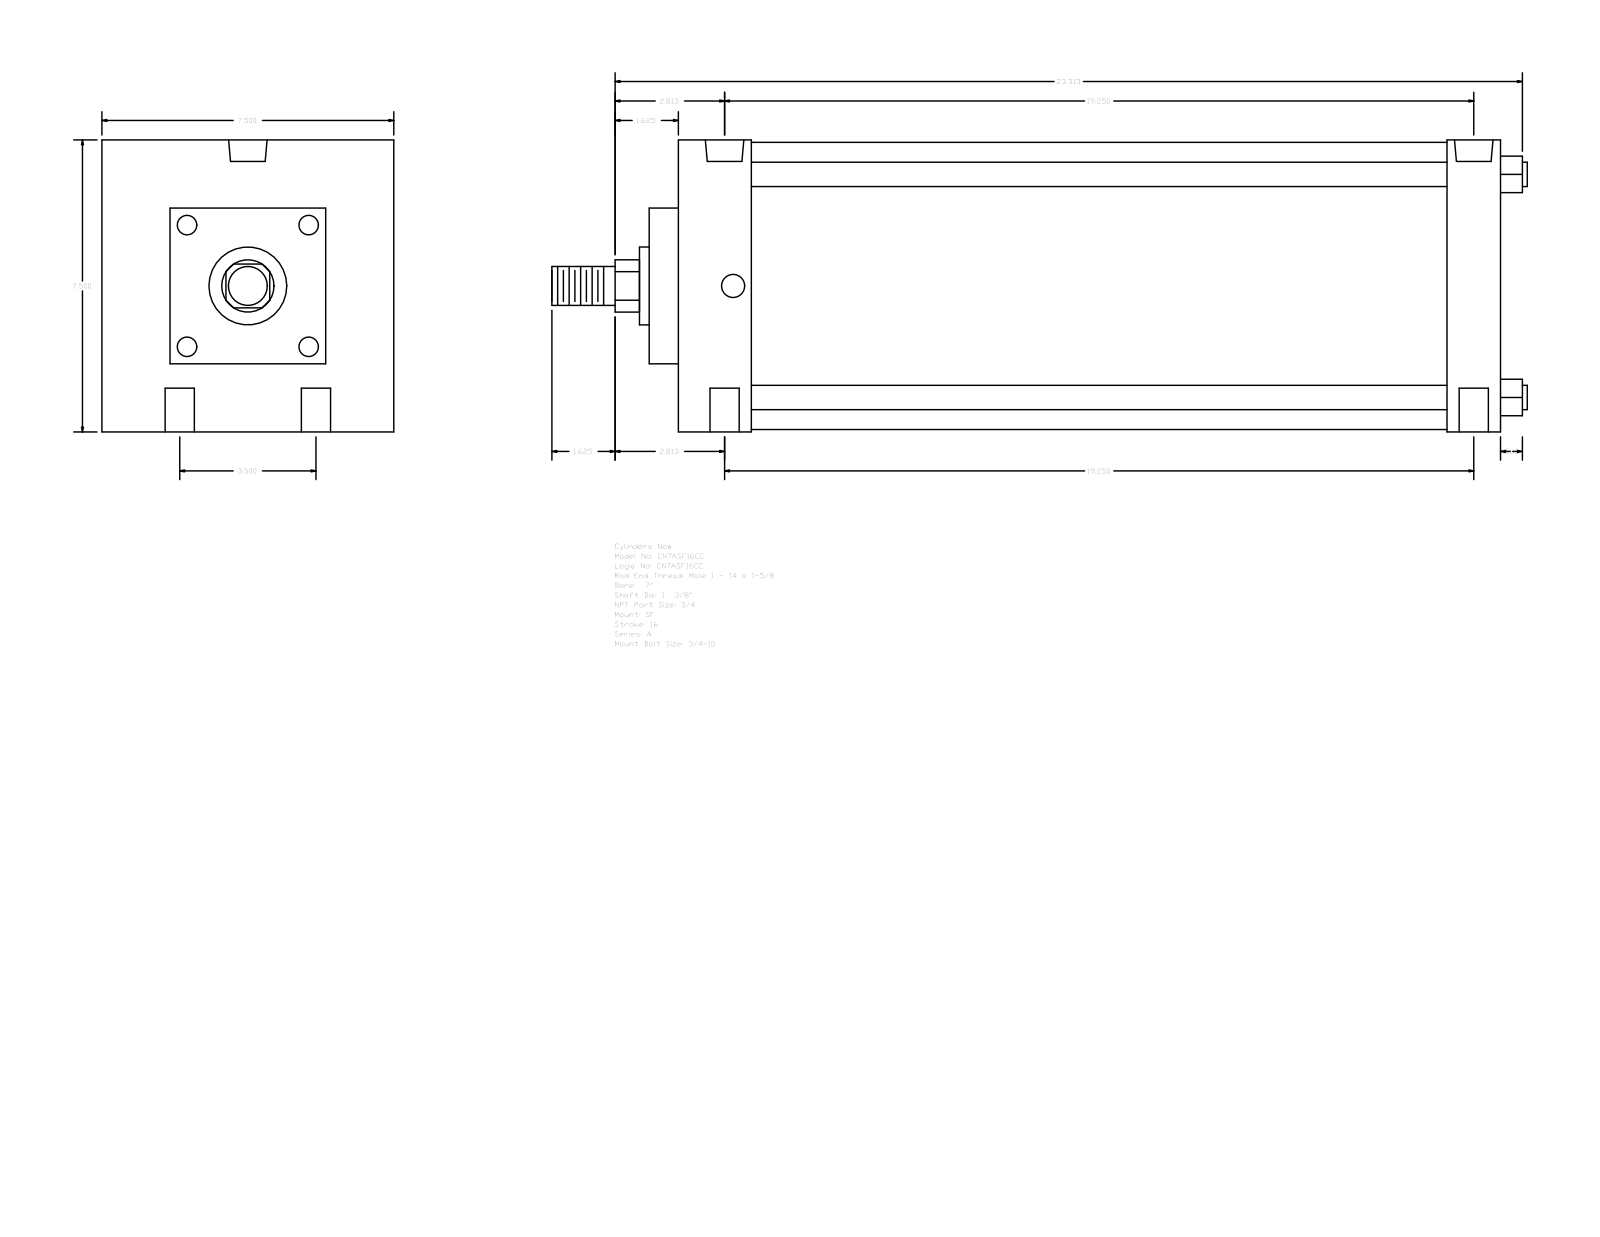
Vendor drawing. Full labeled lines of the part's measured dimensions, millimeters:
Part name (STEP PRODUCT): A_SF__0700_1.375
STEP written by: GSSL Pune (CONFIG_CONTROL_DESIGN)
Units: millimetres
Bodies: 0 solids, 93 faces (67 planar, 26 cylindrical, 0 other)
Overall size (bounding box): 636.59 × 190.5 × 190.5
Round holes (diameter × count): ⌀19.05 ×4, ⌀15.08 ×2, ⌀25.12 ×2
Round bosses / shafts (diameter × count): ⌀15.88 ×4, ⌀187.32 ×1, ⌀50.8 ×1, ⌀34.92 ×1, ⌀25.4 ×1
Partial cylindrical surfaces — rounded edges, fillets, slot ends (radius × count): R17.06 ×1
Main face-to-face distances: 190.5, 536.58, 19.04, 555.62, 66.67, 520.69, 47.63, 501.65, 454.02, 488.95
Hole centre spacings: 44.45, 490.97, 488.95, 88.9, 496.97, 477.83
